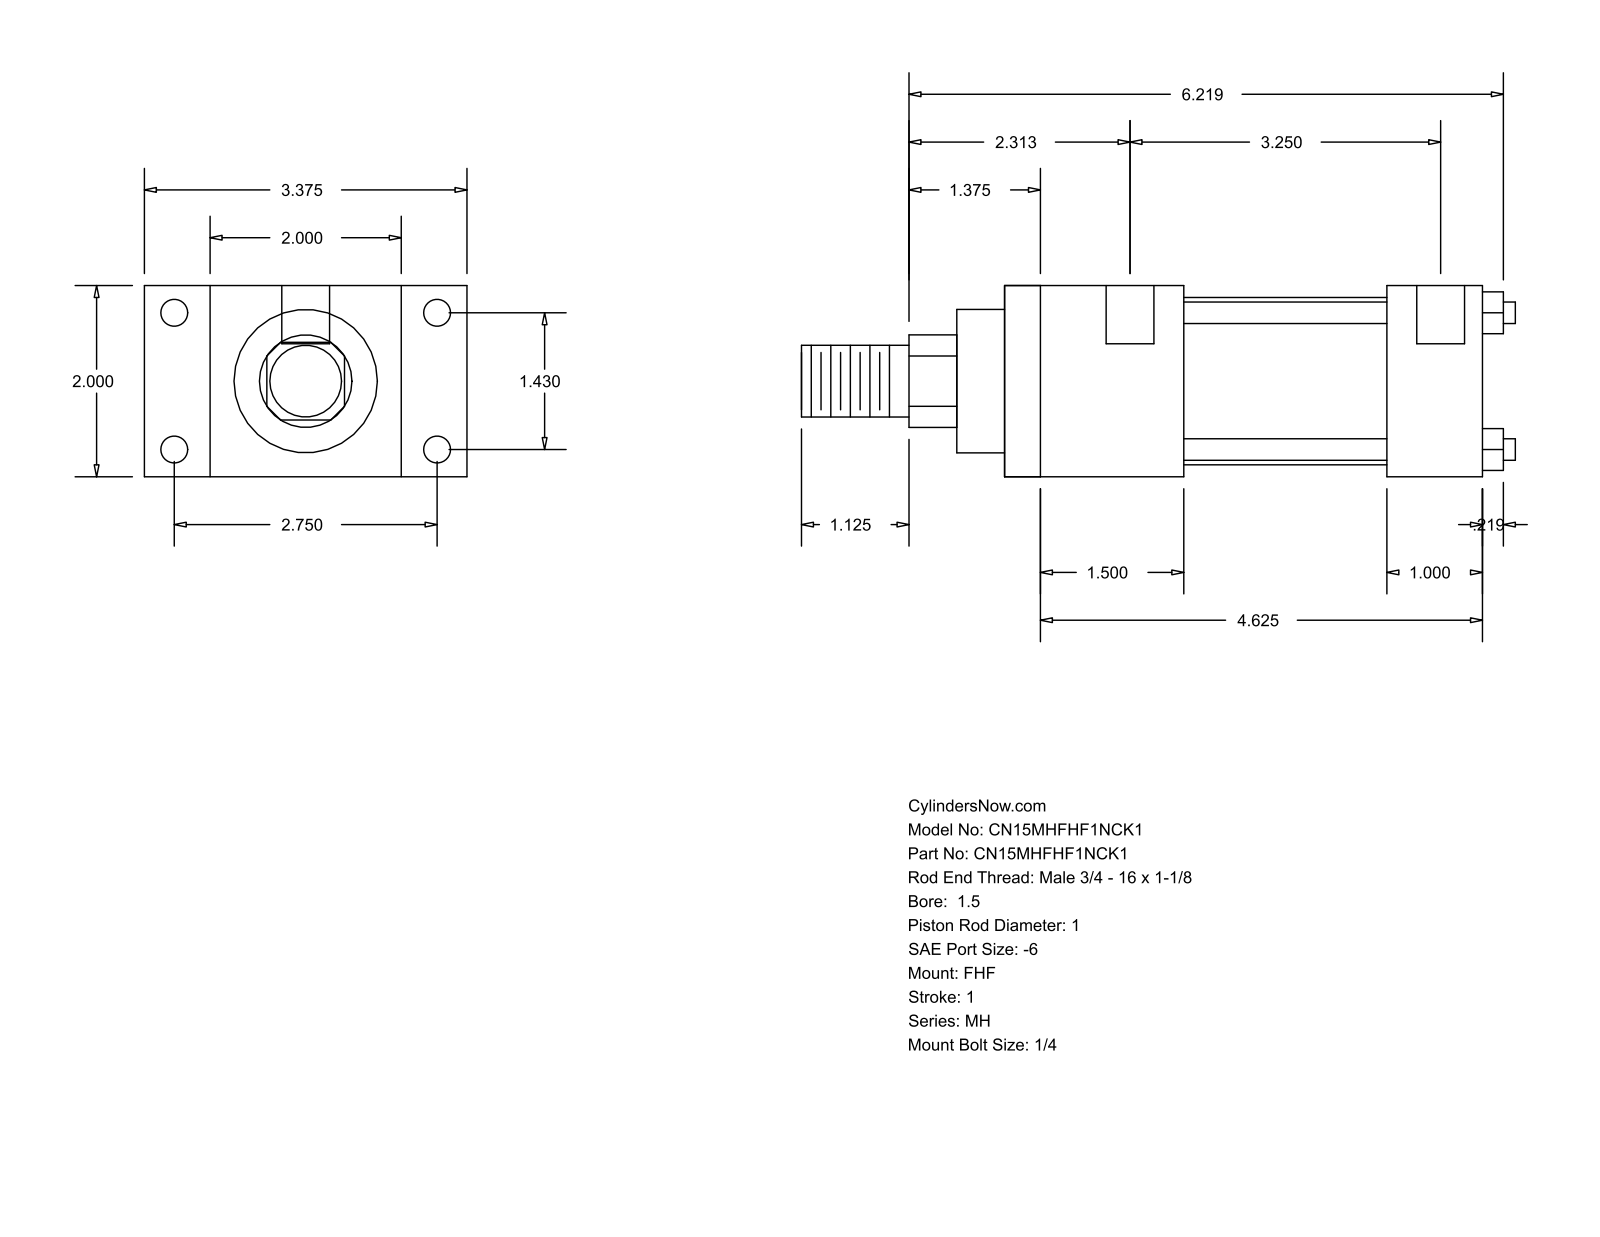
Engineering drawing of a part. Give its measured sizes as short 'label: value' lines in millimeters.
name: MH_FHF__0150_1
written by: GSSL Pune (CONFIG_CONTROL_DESIGN)
unit: mm
bodies: 0 solids, 88 faces (60 planar, 28 cylindrical, 0 other)
size: 189.71 × 85.72 × 50.8
holes: 4× ⌀5.56, 4× ⌀7.14, 2× ⌀12.7
bosses: 4× ⌀5.71, 1× ⌀44.45, 1× ⌀38.1, 1× ⌀25.4, 1× ⌀19.05
rounds: 1× R12.29
face distances: 50.8, 17.46, 68.26, 47.63, 85.72, 127, 79.37, 53.97, 101.6, 25.4
hole spacings: 36.32, 69.84, 78.72, 85.73, 3.18, 82.55
